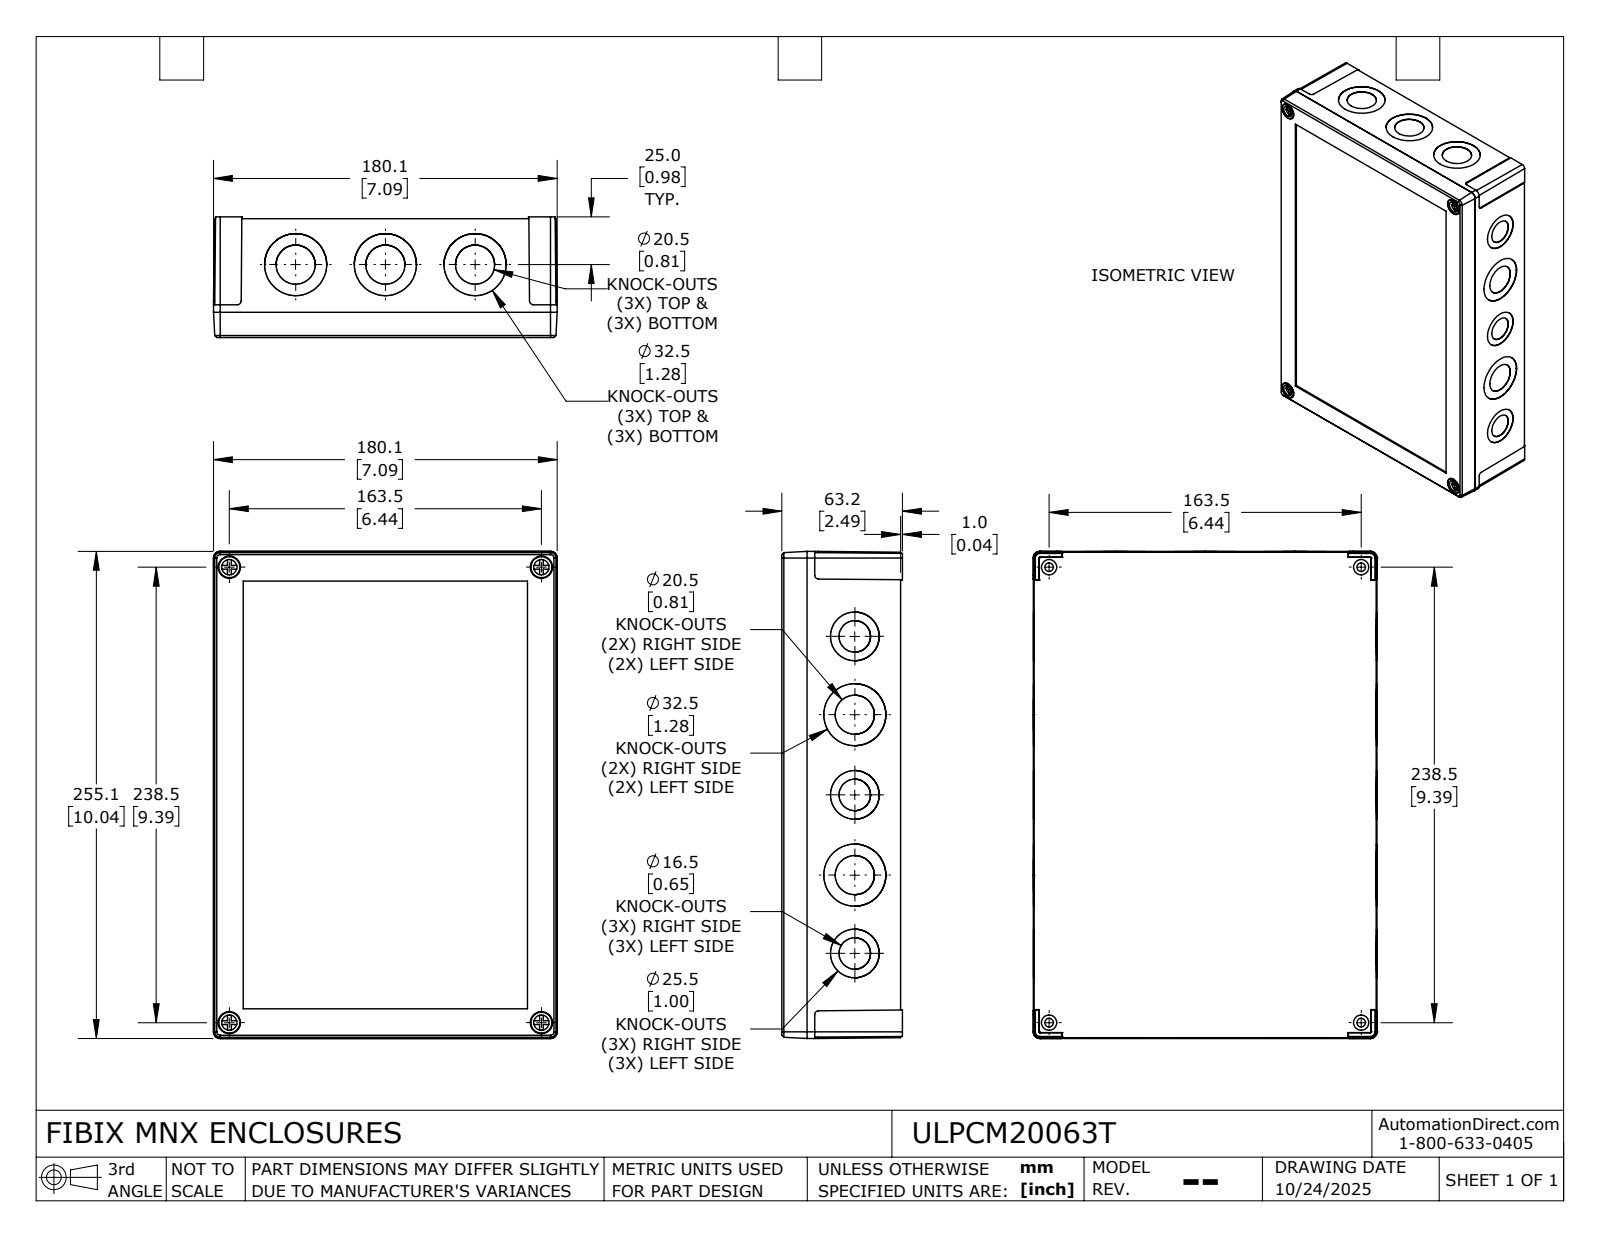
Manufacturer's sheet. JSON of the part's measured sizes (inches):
{"part_name": "ULPCM20063T_Default", "step_written_by": "SolidWorks 2024 (CONFIG_CONTROL_DESIGN)", "units": "inches", "bodies": {"solids": 6, "faces": 795, "planar": 397, "cylindrical": 350, "other": 48}, "overall_size": [10.043, 7.091, 2.488], "volume_in3": 36.25, "surface_area_in2": 476.9, "round_holes": [[0.126, 40], [0.094, 20], [0.157, 20], [0.807, 10], [1.28, 10], [0.65, 6], [1.004, 6], [0.177, 4], [0.315, 4], [0.457, 4]], "round_bosses_or_shafts": [[0.315, 16], [0.433, 4], [0.283, 4], [0.276, 4]], "partial_cylinders_radius": [[0.112, 6], [0.042, 4], [0.079, 4], [0.197, 4], [0.046, 2], [48.383, 1]], "face_to_face_distances": [0.118, 2.409, 2.291, 0.138, 2.272, 2.154, 0.165, 0.039, 0.177, 2.449], "hole_center_spacings": [4.921, 1.939, 1.969, 5.046, 3.937, 0.812, 0.872, 1.046]}
